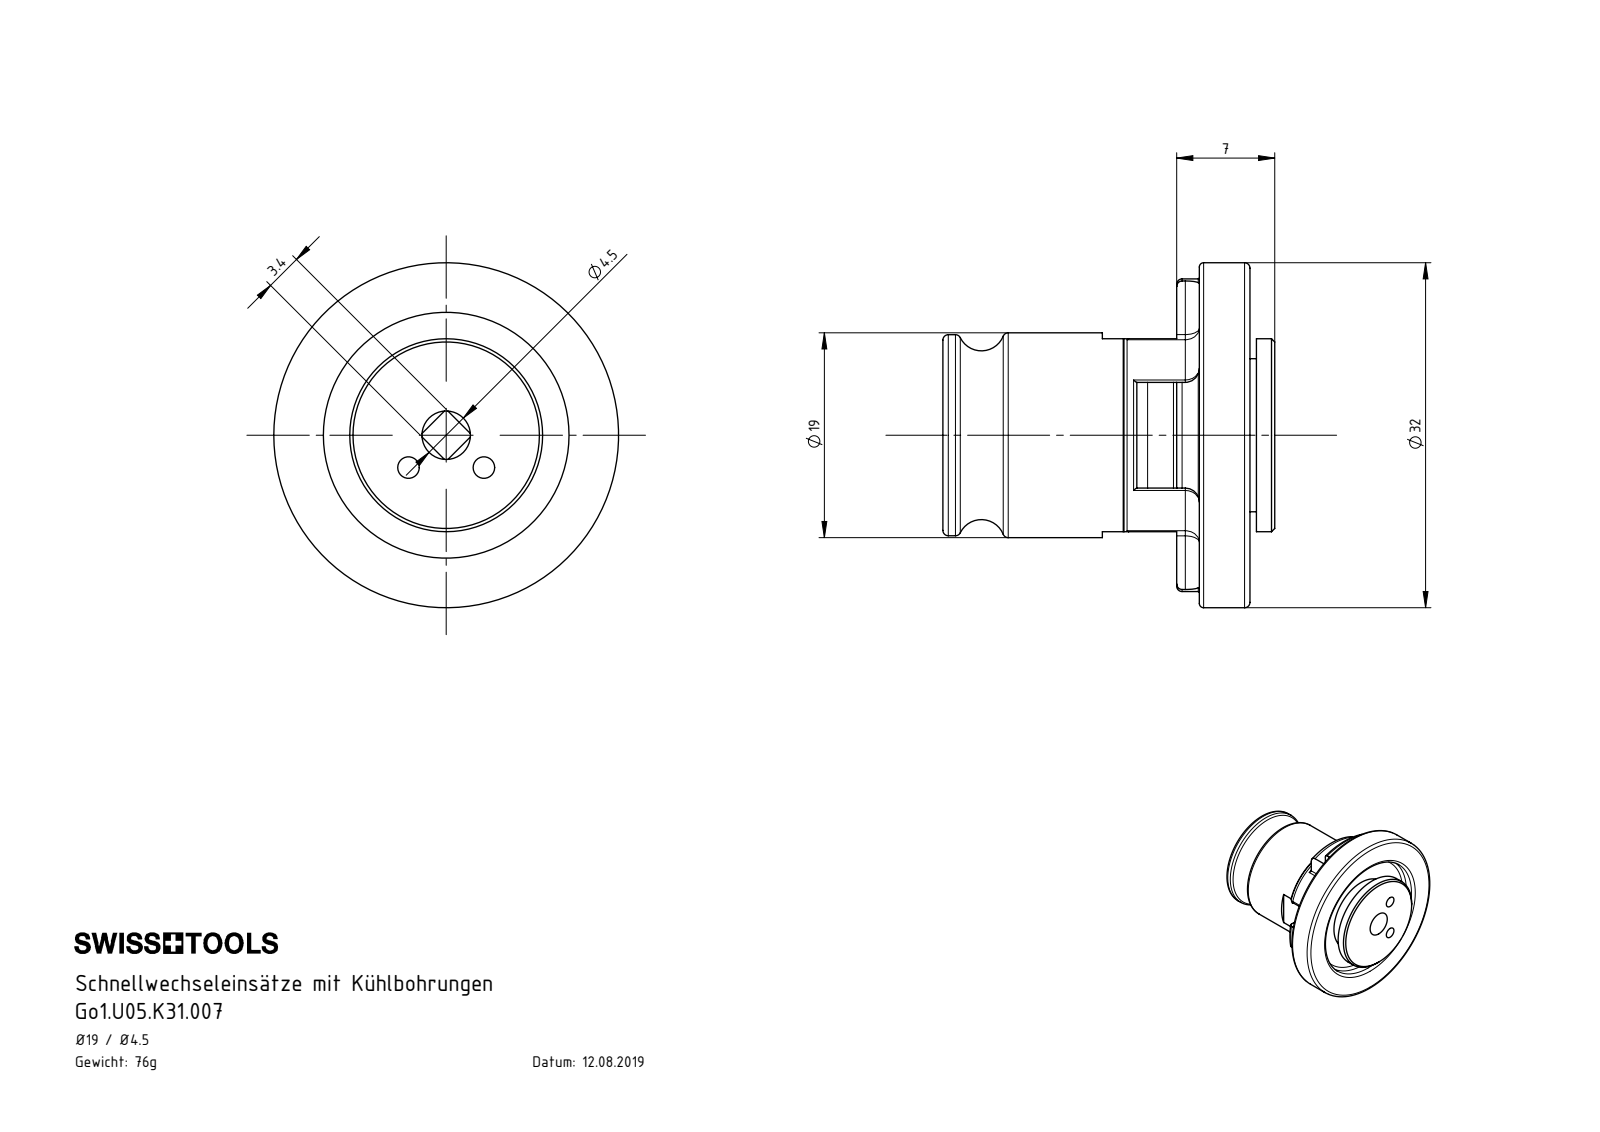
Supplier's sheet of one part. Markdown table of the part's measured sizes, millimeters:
| quantity | value |
| --- | --- |
| part name | Go1.U05.K31.007 |
| STEP written by | SolidWorks 2017 (AUTOMOTIVE_DESIGN) |
| units | millimeters |
| bodies | 1 solid, 114 faces (36 planar, 34 cylindrical, 44 other) |
| overall size | 32 × 32 × 30.8 |
| volume | 9 621 mm³ |
| surface area | 4 837 mm² |
| round holes (diameter × count) | 2 × 2, 4.5 × 1, 11.4 × 1, 22.8 × 1 |
| round bosses / shafts (diameter × count) | 32 × 1, 19 × 1, 18.65 × 1, 18.52 × 1, 17.9 × 1, 14.2 × 1 |
| partial cylindrical surfaces (radius × count) | 0.5 × 8, 1.3 × 4, 12.4 × 1, 14.5 × 1 |
| main face-to-face distances | 2.35, 4.7, 7, 4.65, 2.3, 23.8, 26.15, 28.5, 30.8, 29.1 |
| hole center spacings | 4.61, 7 |
